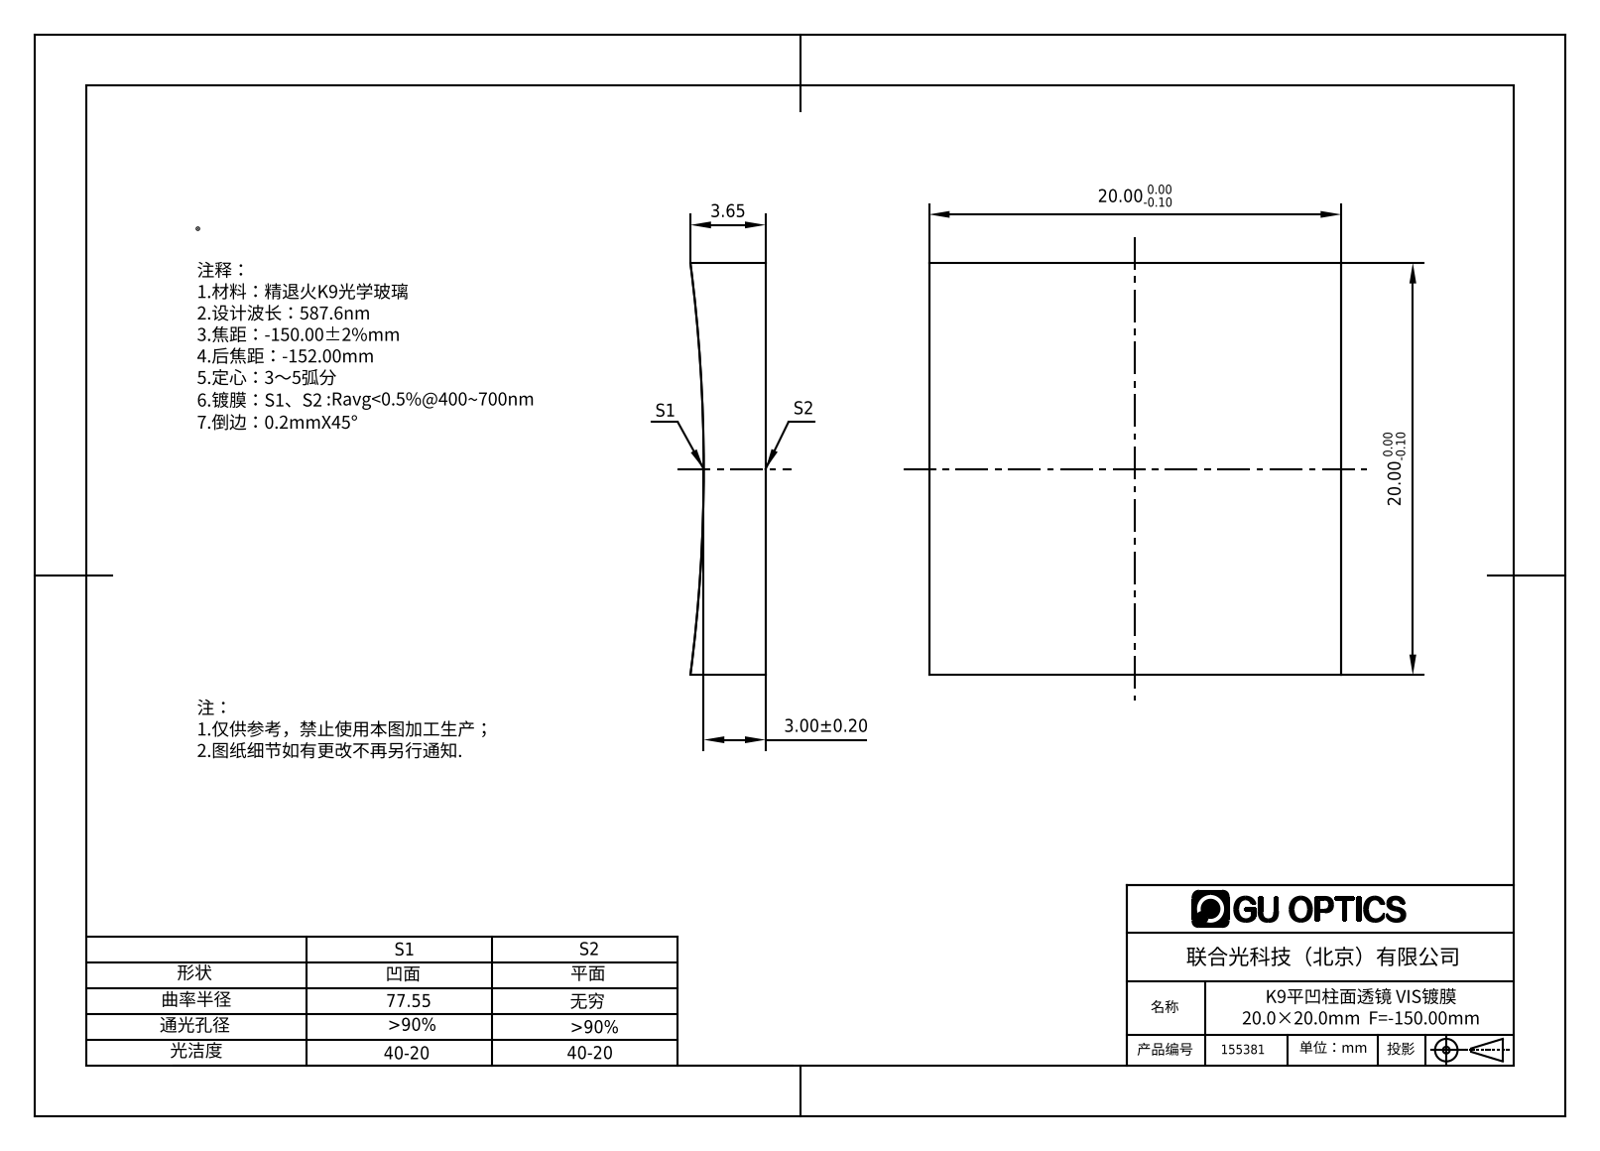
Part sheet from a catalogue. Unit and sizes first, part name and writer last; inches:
Units: inches
Overall size (bounding box): 0.787 × 0.787 × 0.144
Partial cylindrical surfaces — rounded edges, fillets, slot ends (radius × count): R3.053 ×1
Main face-to-face distances: 0.787
Volume: 0.078 in³ · Surface area: 1.668 in²
Bodies: 1 solid, 6 faces (5 planar, 1 cylindrical, 0 other)
Part name (STEP PRODUCT): 155348
STEP written by: SolidWorks 2016 (AUTOMOTIVE_DESIGN)
